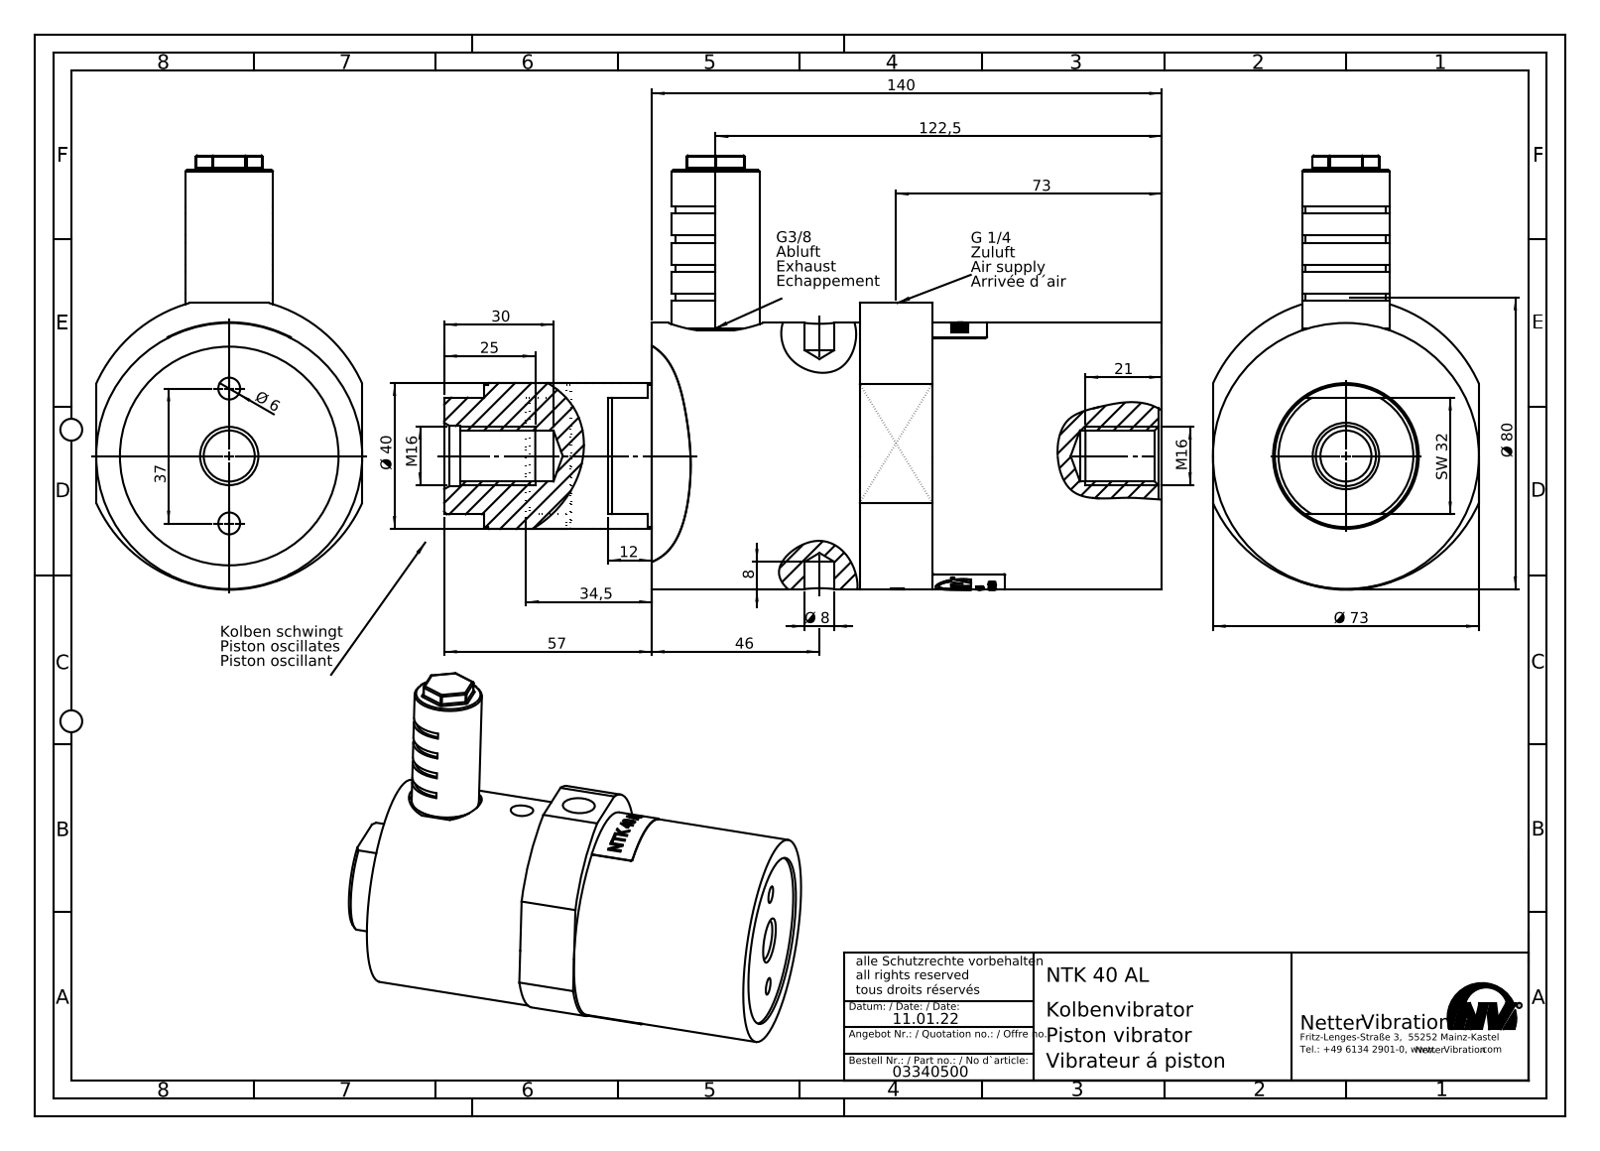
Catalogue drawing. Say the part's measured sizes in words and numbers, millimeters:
The part is named "NTK 40 AL #03340500". Its 3-D file was written by "SolidWorks 2015 (AUTOMOTIVE_DESIGN)". It is 2 solids with 169 faces: 49 planar, 80 cylindrical and 40 other. Overall it measures 152 by 117 by 73 millimeters. Its volume is 619 372 cubic millimeters and its surface area 52 651 square millimeters. Round holes: 2 of diameter 6, 1 of diameter 8, 1 of diameter 11.45, 1 of diameter 14, 1 of diameter 14.95, 1 of diameter 16.5, 1 of diameter 40, 1 of diameter 60. Round bosses or shafts: 1 of diameter 73, 1 of diameter 39, 1 of diameter 24, 1 of diameter 16.66. Partial cylindrical surfaces (rounded edges, fillets, slot ends): 22 of radius 0.5, 1 of radius 11, 1 of radius 13, 1 of radius 36.7, 1 of radius 40. The main face-to-face distances are 139, 1, 140, 12, 57, 151, 152, 20, 83, 82. The hole center spacings are 18.5, 21, 28.7, 37, 49.7.
